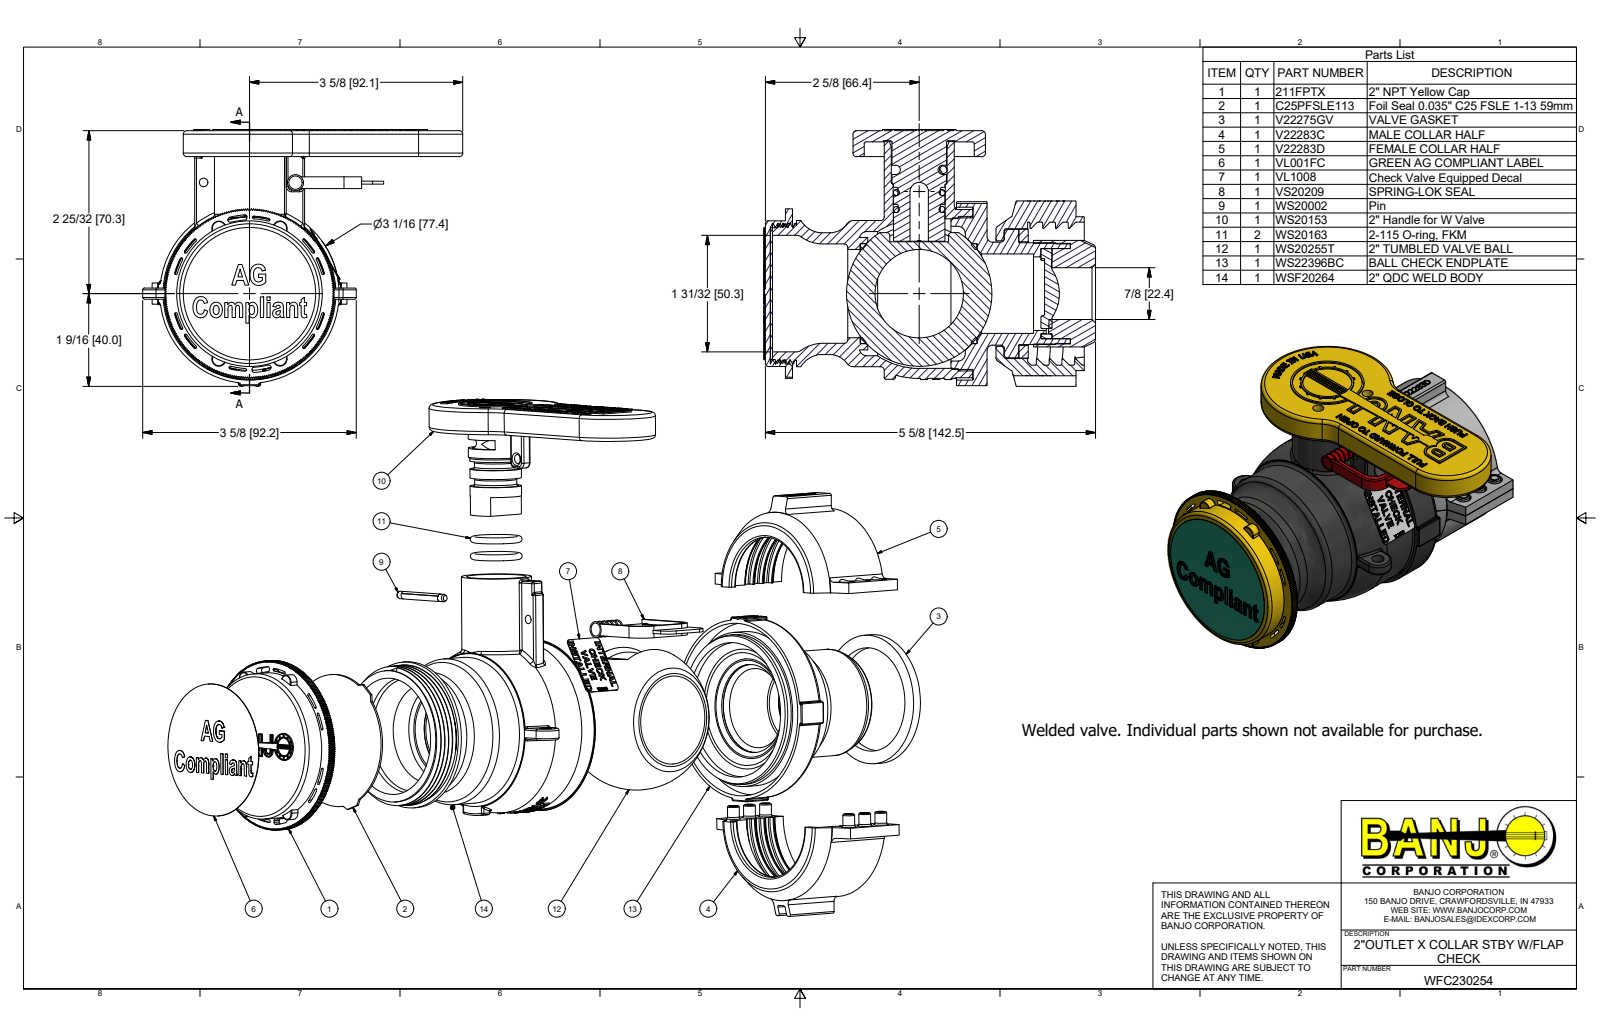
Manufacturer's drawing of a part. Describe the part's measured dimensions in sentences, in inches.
The part is named "WFC230254; WSF20264; WSF20264X; V22275GV (+8 more)". Its 3-D file was written by "Autodesk Inventor 2018 (AUTOMOTIVE_DESIGN)". It is 20 solids with 4433 faces: 2291 planar, 979 cylindrical and 1163 other. Overall it measures 5.638 by 5.44 by 4.363 inches. Its volume is 21.45 cubic inches and its surface area 285.3 square inches. Round holes: 6 of diameter 0.209, 6 of diameter 0.257, 2 of diameter 0.145, 2 of diameter 0.188, 2 of diameter 0.207, 2 of diameter 1.187, 2 of diameter 1.5, 1 of diameter 0.156, 1 of diameter 0.309, 1 of diameter 0.312, 1 of diameter 0.436, 1 of diameter 0.837. Round bosses or shafts: 6 of diameter 0.2, 2 of diameter 2.25, 1 of diameter 3.047, 1 of diameter 2.91, 1 of diameter 2.88, 1 of diameter 2.858, 1 of diameter 2.625, 1 of diameter 2.615. Partial cylindrical surfaces (rounded edges, fillets, slot ends): 77 of radius 0.03, 36 of radius 0.015, 10 of radius 0.09, 4 of radius 0.06, 4 of radius 0.062, 4 of radius 0.118, 4 of radius 0.25, 3 of radius 0.01. The main face-to-face distances are 0.02, 0.12, 0.035, 0.085, 0.14, 0.105, 0.19, 3.649, 3.684, 3.769. The hole center spacings are 2.881, 2.857, 0.375, 0.375, 0.75, 1.562, 1.633, 2.045.
